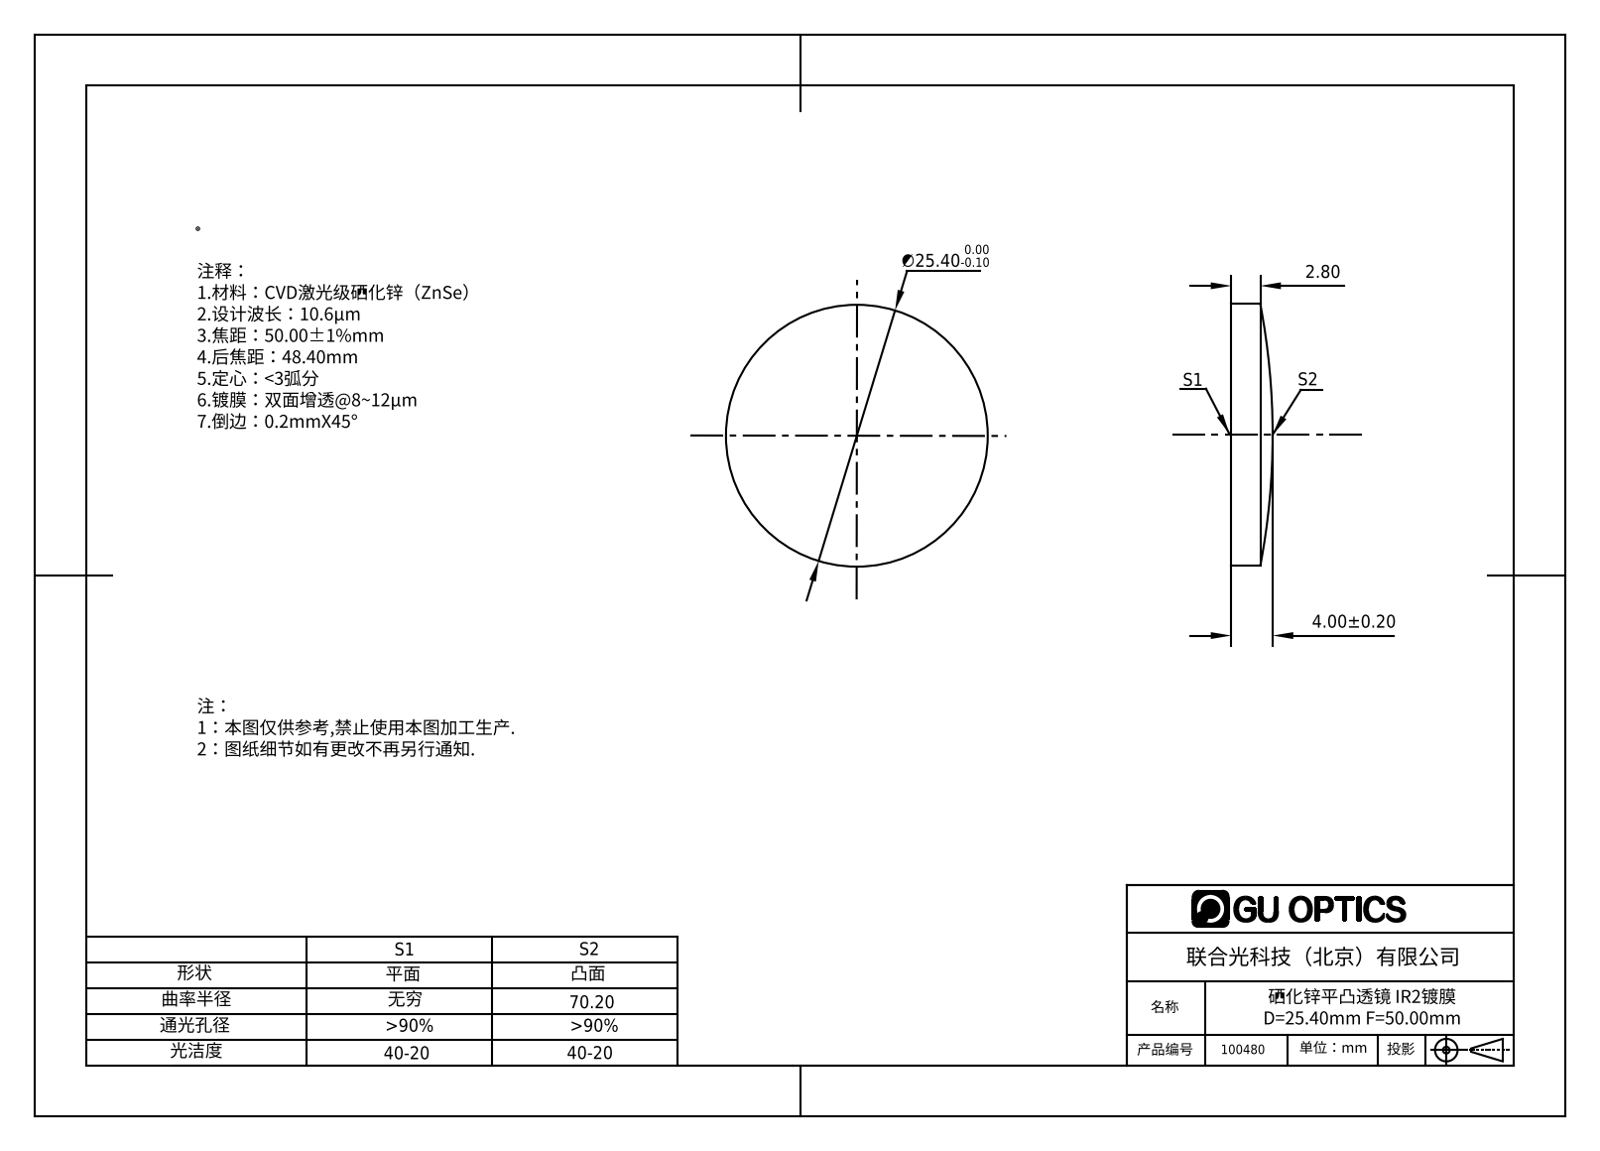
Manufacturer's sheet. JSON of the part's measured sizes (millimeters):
{"part_name": "100468", "step_written_by": "SolidWorks 2016 (AUTOMOTIVE_DESIGN)", "units": "millimeters", "bodies": {"solids": 1, "faces": 5, "planar": 1, "cylindrical": 2, "other": 2}, "overall_size": [12.7, 12.7, 2], "volume_mm3": 215, "surface_area_mm2": 310, "round_bosses_or_shafts": [[12.7, 1]]}
